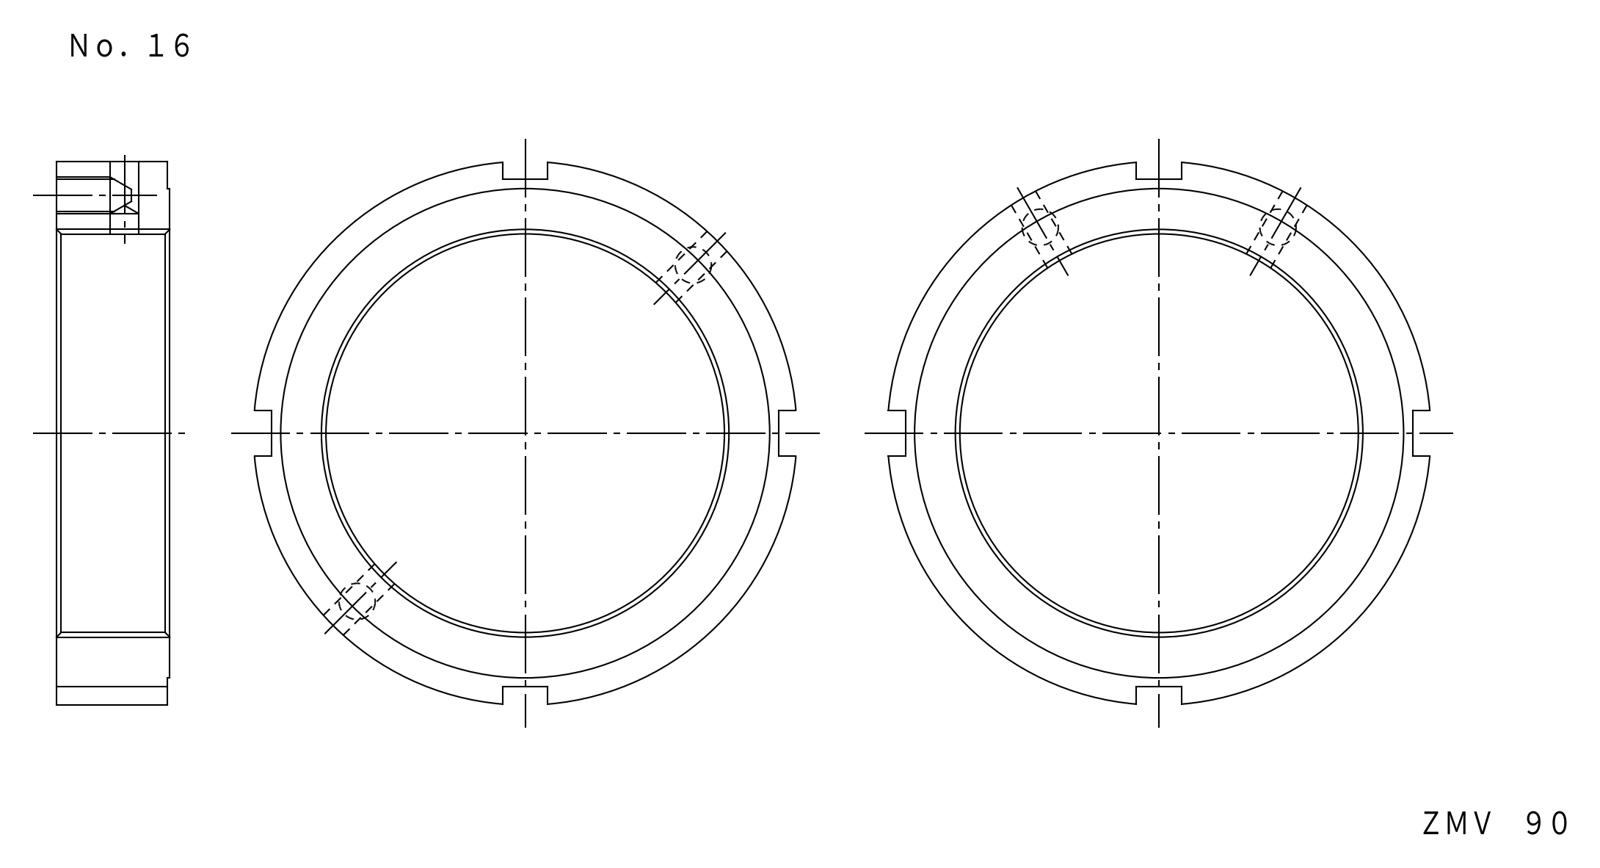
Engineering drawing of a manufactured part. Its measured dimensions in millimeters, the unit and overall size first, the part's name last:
Units: millimetres
Overall size (bounding box): 119.58 × 119.58 × 25
Round holes (diameter × count): ⌀6.2 ×2, ⌀6.65 ×2, ⌀90 ×1
Round bosses / shafts (diameter × count): ⌀120 ×1, ⌀108 ×1
Main face-to-face distances: 25, 0.5, 24.5, 51, 61, 112, 10
Hole centre spacings: 52.5, 104.99
Volume: 117 002 mm³ · Surface area: 27 655 mm²
Bodies: 1 solid, 29 faces (15 planar, 10 cylindrical, 4 other)
Part name (STEP PRODUCT): FKD ZMV90
STEP written by: Autodesk Inventor LT (CONFIG_CONTROL_DESIGN)
